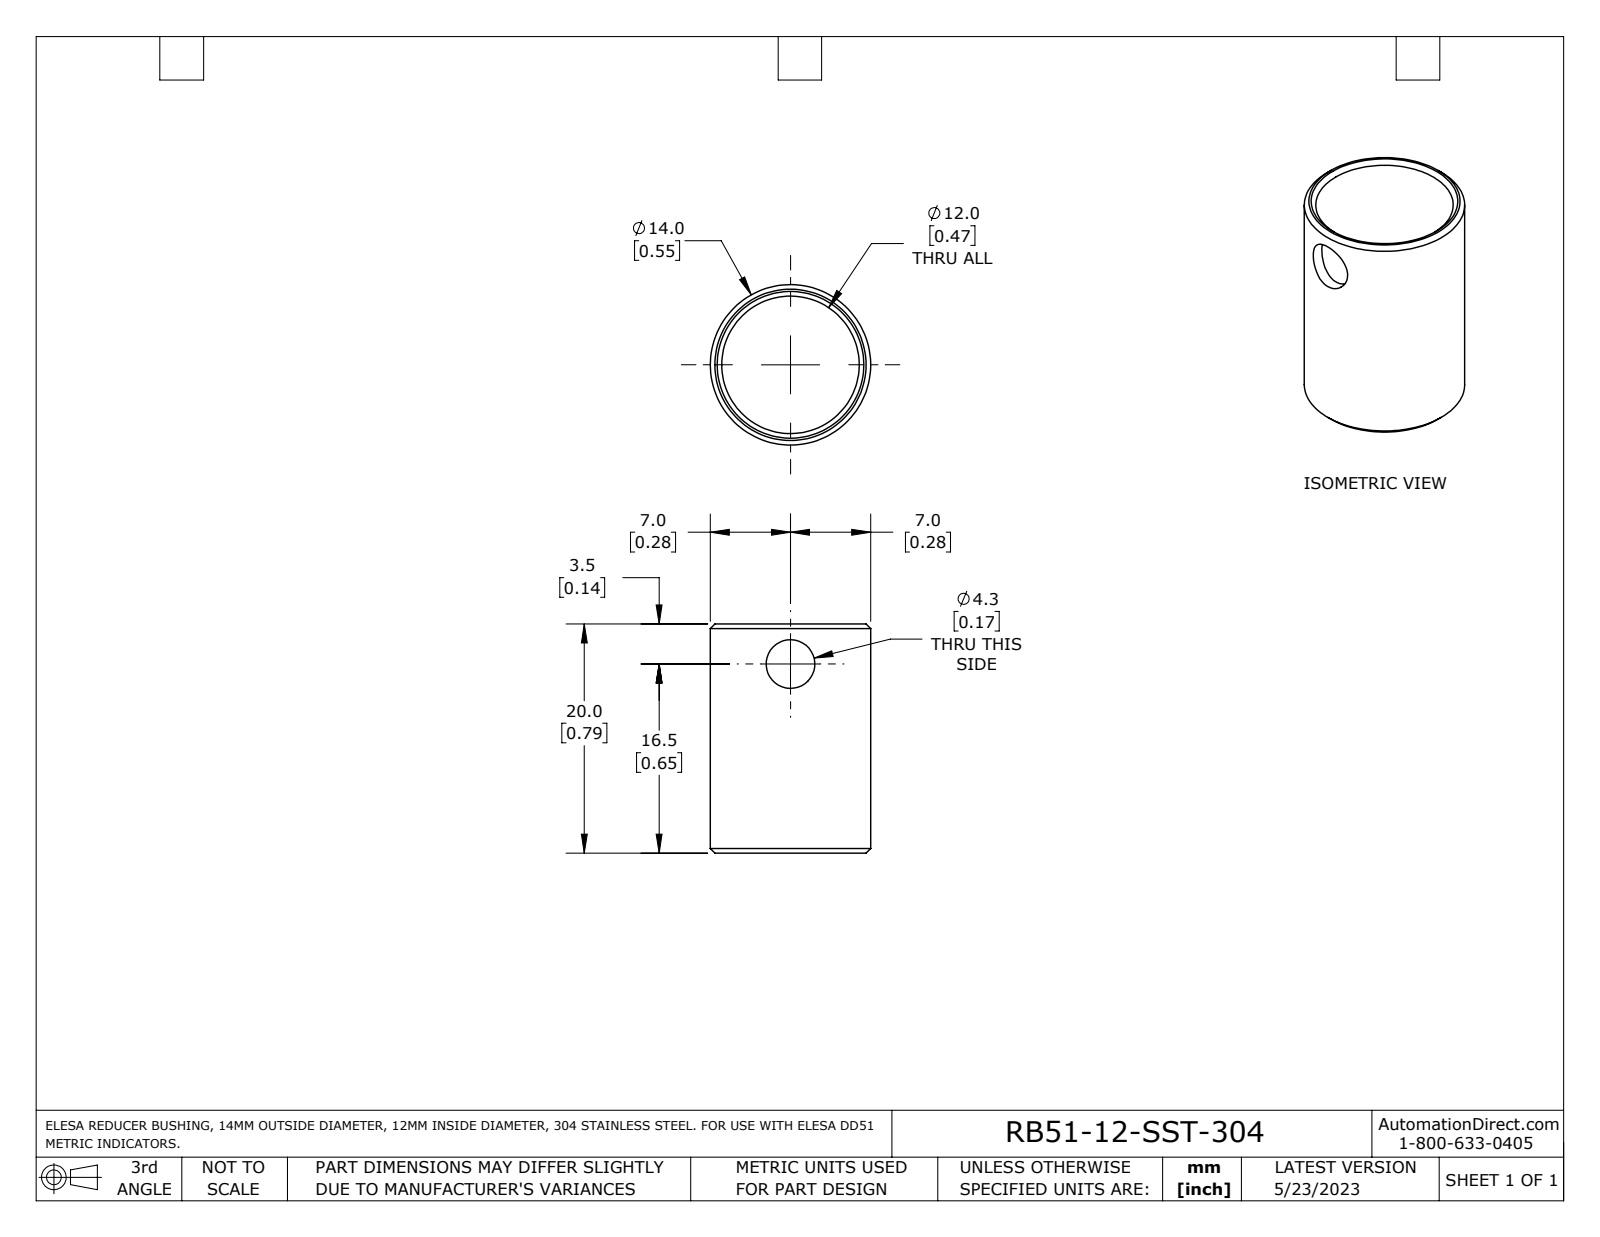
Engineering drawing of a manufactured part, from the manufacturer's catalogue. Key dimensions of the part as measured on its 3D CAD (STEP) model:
Part name (STEP PRODUCT): RB51-12-SST-304
STEP written by: SolidWorks 2021 (AUTOMOTIVE_DESIGN)
Units: inches
Bodies: 1 solid, 9 faces (2 planar, 3 cylindrical, 4 other)
Overall size (bounding box): 0.787 × 0.551 × 0.551
Volume: 0.048 in³ · Surface area: 2.576 in²
Round holes (diameter × count): ⌀0.167 ×1, ⌀0.472 ×1
Round bosses / shafts (diameter × count): ⌀0.551 ×1
Main face-to-face distances: 0.787
